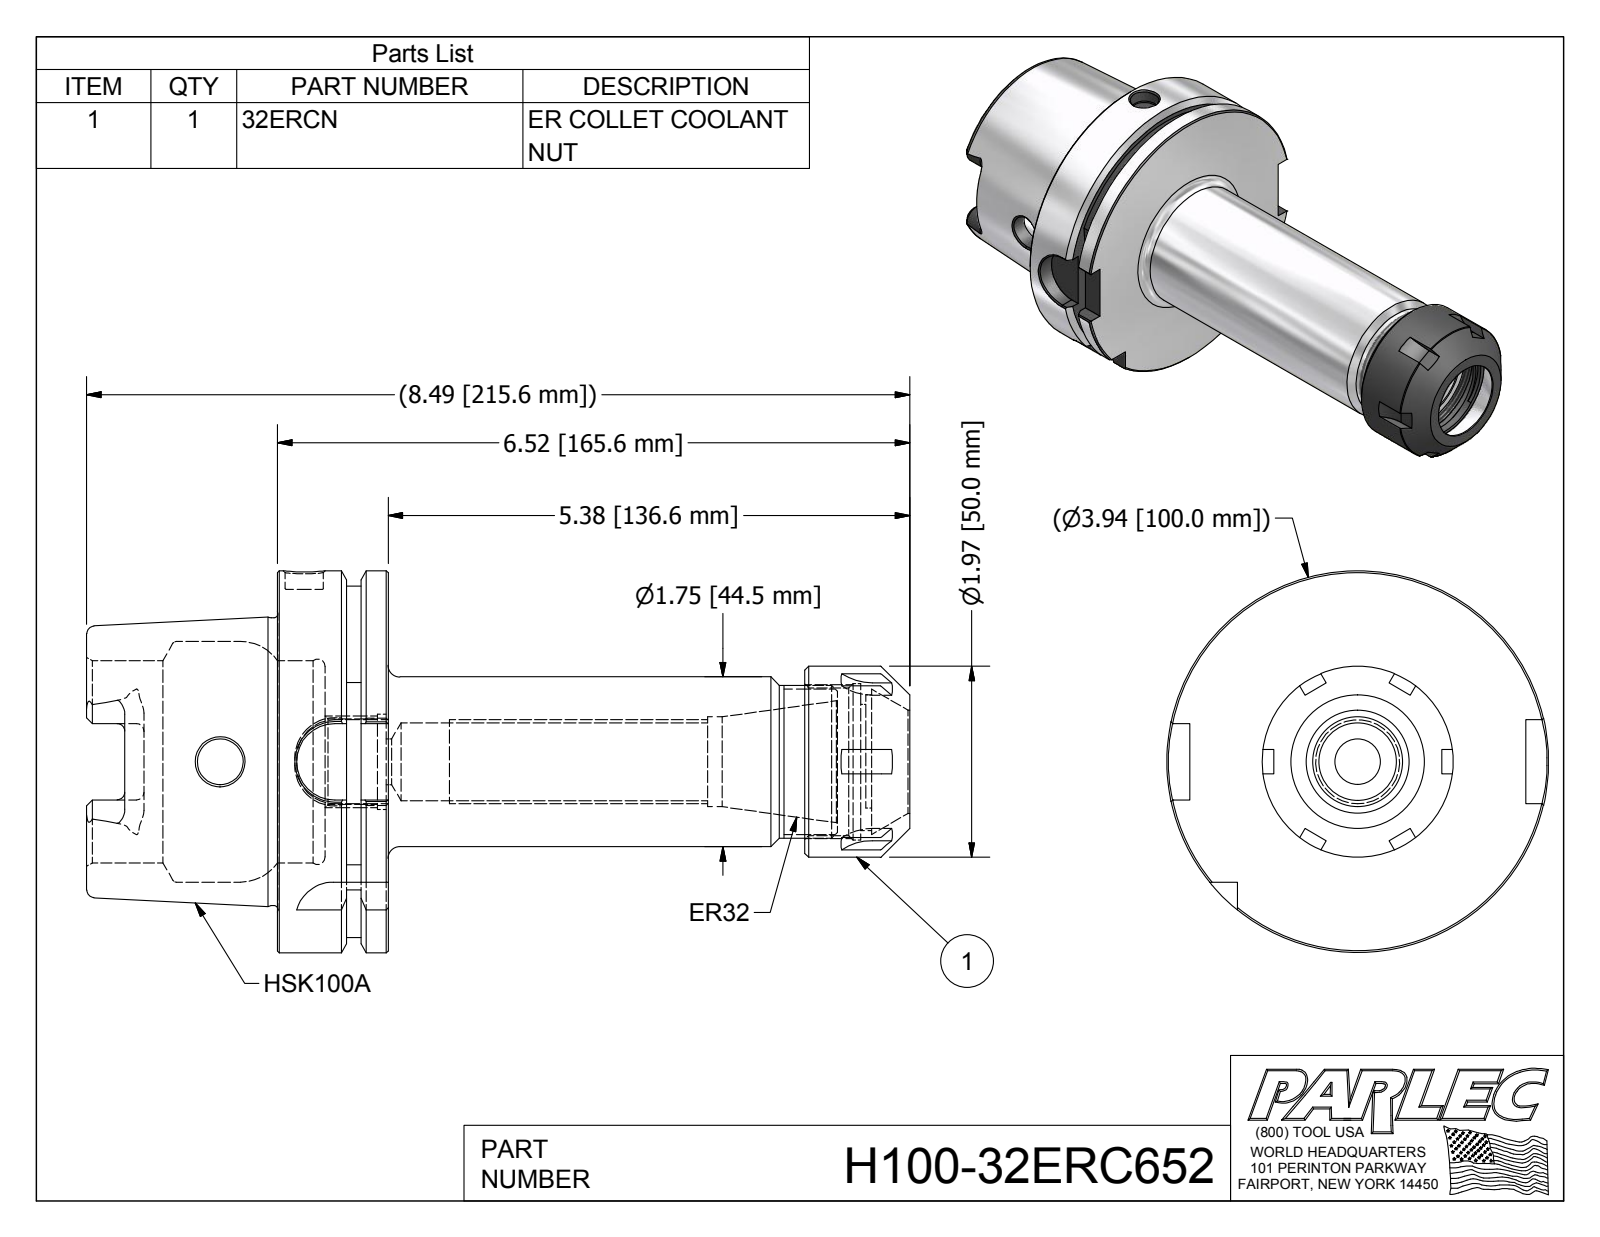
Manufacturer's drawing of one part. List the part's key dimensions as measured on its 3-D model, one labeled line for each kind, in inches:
Part name (STEP PRODUCT): H100-32ERC652; H100-32ER630-1; 32ERCN
STEP written by: Autodesk Inventor 2012 (AUTOMOTIVE_DESIGN)
Units: inches
Bodies: 2 solids, 174 faces (66 planar, 47 cylindrical, 61 other)
Overall size (bounding box): 8.489 × 3.937 × 3.937
Volume: 24.72 in³ · Surface area: 129.1 in²
Round holes (diameter × count): ⌀0.472 ×2, ⌀0.394 ×1, ⌀0.802 ×1, ⌀0.881 ×1, ⌀0.925 ×1, ⌀0.985 ×1, ⌀1.063 ×1, ⌀1.299 ×1, ⌀1.522 ×1, ⌀1.614 ×1, ⌀2.087 ×1, ⌀2.48 ×1
Round bosses / shafts (diameter × count): ⌀3.937 ×1, ⌀2.967 ×1, ⌀1.969 ×1, ⌀1.75 ×1, ⌀1.575 ×1
Partial cylindrical surfaces — rounded edges, fillets, slot ends (radius × count): R0.079 ×6, R0.5 ×6, R0.192 ×4, R0.394 ×4, R0.689 ×1, R1.811 ×1
Main face-to-face distances: 1.142, 0.492, 0.65, 1.969, 2.461, 3.11, 2.83, 0.861, 0.369, 0.28
Hole centre spacings: 0.059
